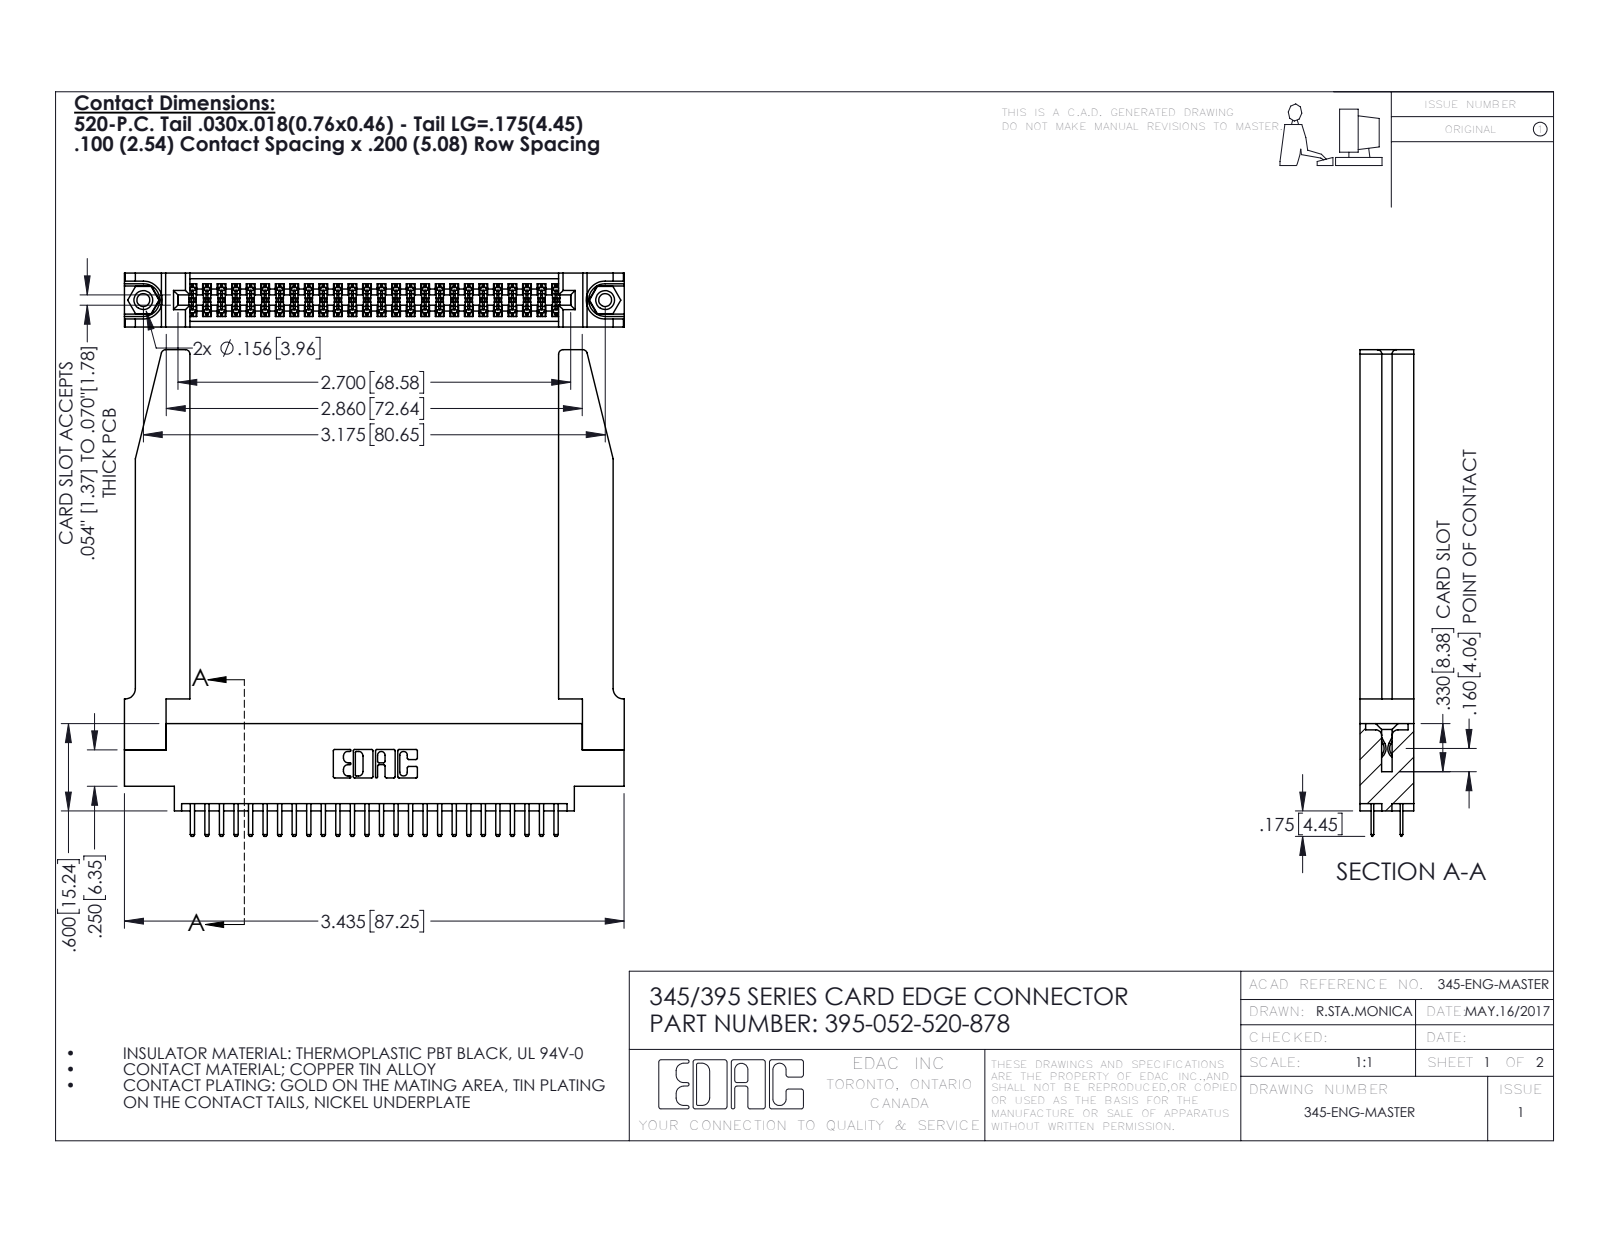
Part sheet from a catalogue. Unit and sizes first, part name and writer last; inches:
Units: inches
Overall size (bounding box): 3.436 × 3.345 × 0.37
Round holes (diameter × count): ⌀0.089 ×2, ⌀0.125 ×2, ⌀0.156 ×2, ⌀0.064 ×1
Round bosses / shafts (diameter × count): ⌀0.155 ×2
Partial cylindrical surfaces — rounded edges, fillets, slot ends (radius × count): R0.006 ×78, R0.01 ×56, R0.01 ×22, R0.03 ×8, R0.007 ×6, R0.031 ×6, R0.026 ×3, R0.014 ×2
Main face-to-face distances: 0.37, 0.072, 0.298, 0.2, 0.098, 0.272, 0.025, 0.225, 0.123, 0.15
Hole centre spacings: 0.27, 2.94, 3.175
Volume: 0.974 in³ · Surface area: 29.04 in²
Bodies: 57 solids, 3172 faces (2046 planar, 1074 cylindrical, 52 other)
Part name (STEP PRODUCT): 345-292-001_345-293-120; 395-052-520-878; 345 Part_0.170 Offset - 0.156 Dia-TH; 345-220-078_345-220-078 (+1 more)
STEP written by: SolidWorks 2016 (CONFIG_CONTROL_DESIGN)
